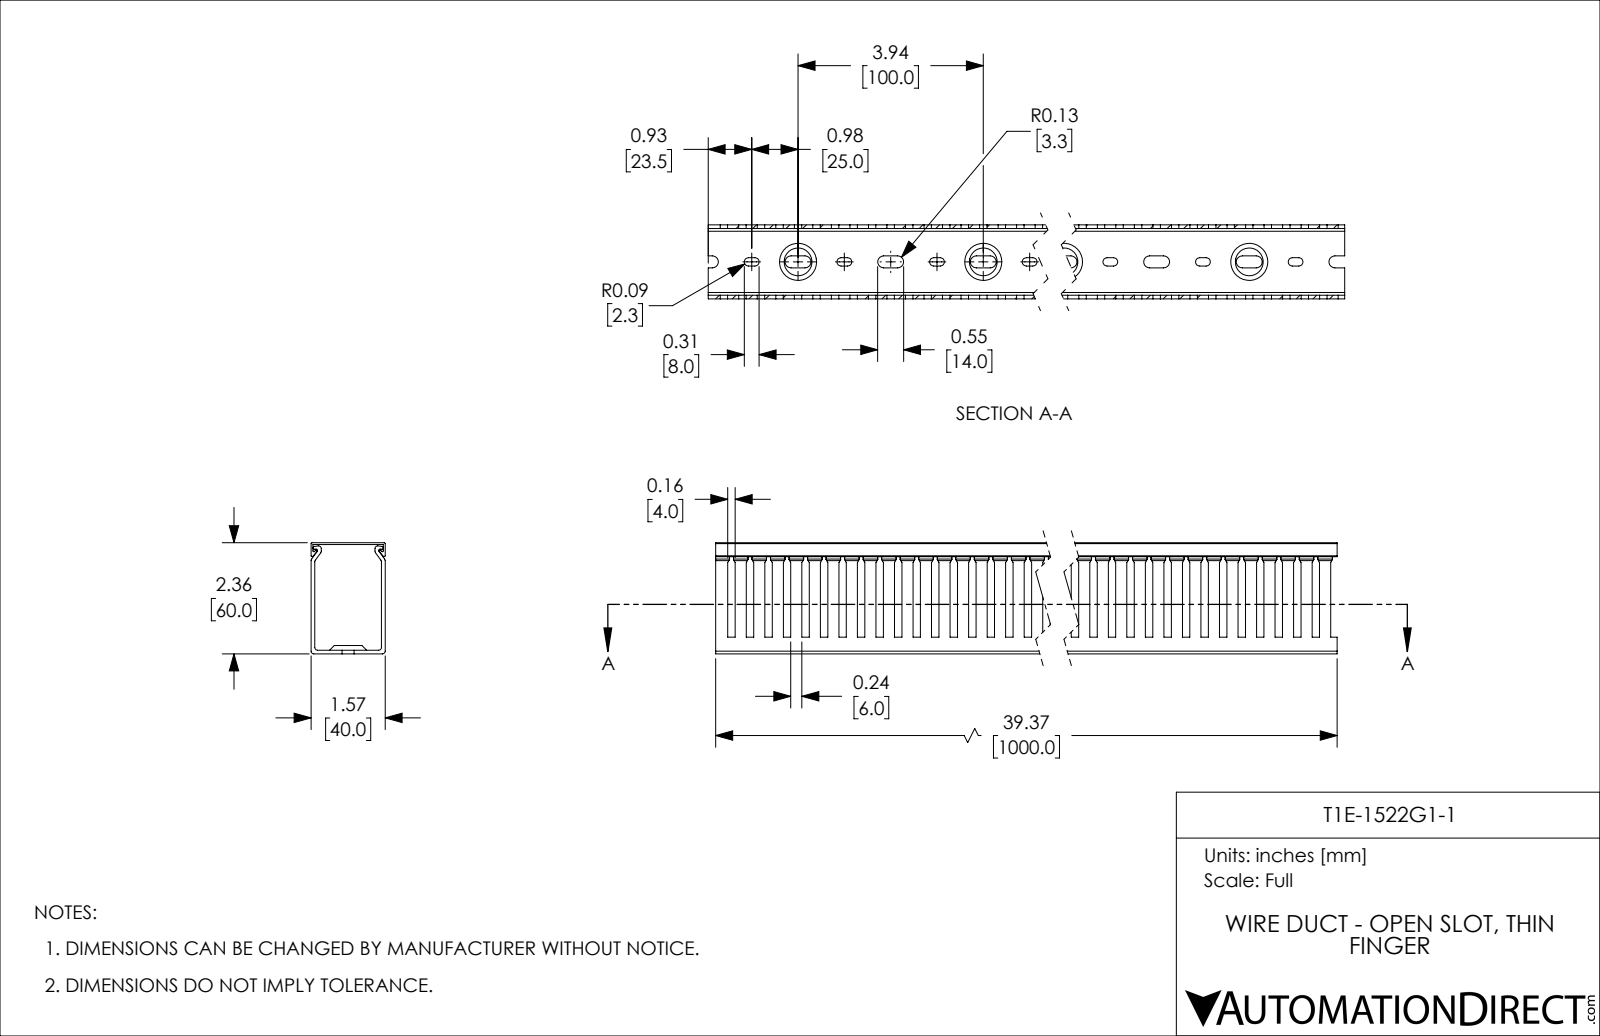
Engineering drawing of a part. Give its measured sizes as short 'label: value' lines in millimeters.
name: T1E-1522G1-1
written by: SolidWorks 2021 (CONFIG_CONTROL_DESIGN)
unit: mm
bodies: 2 solids, 775 faces (444 planar, 311 cylindrical, 20 other)
size: 1000 × 60 × 40
volume: 366 769 mm³; area: 427 595 mm²
rounds: 40× R2.25, 40× R3.25, 12× R1.5, 8× R0.5, 6× R0.75
face distances: 2, 38, 40, 1, 36, 60, 59, 57, 58, 39
